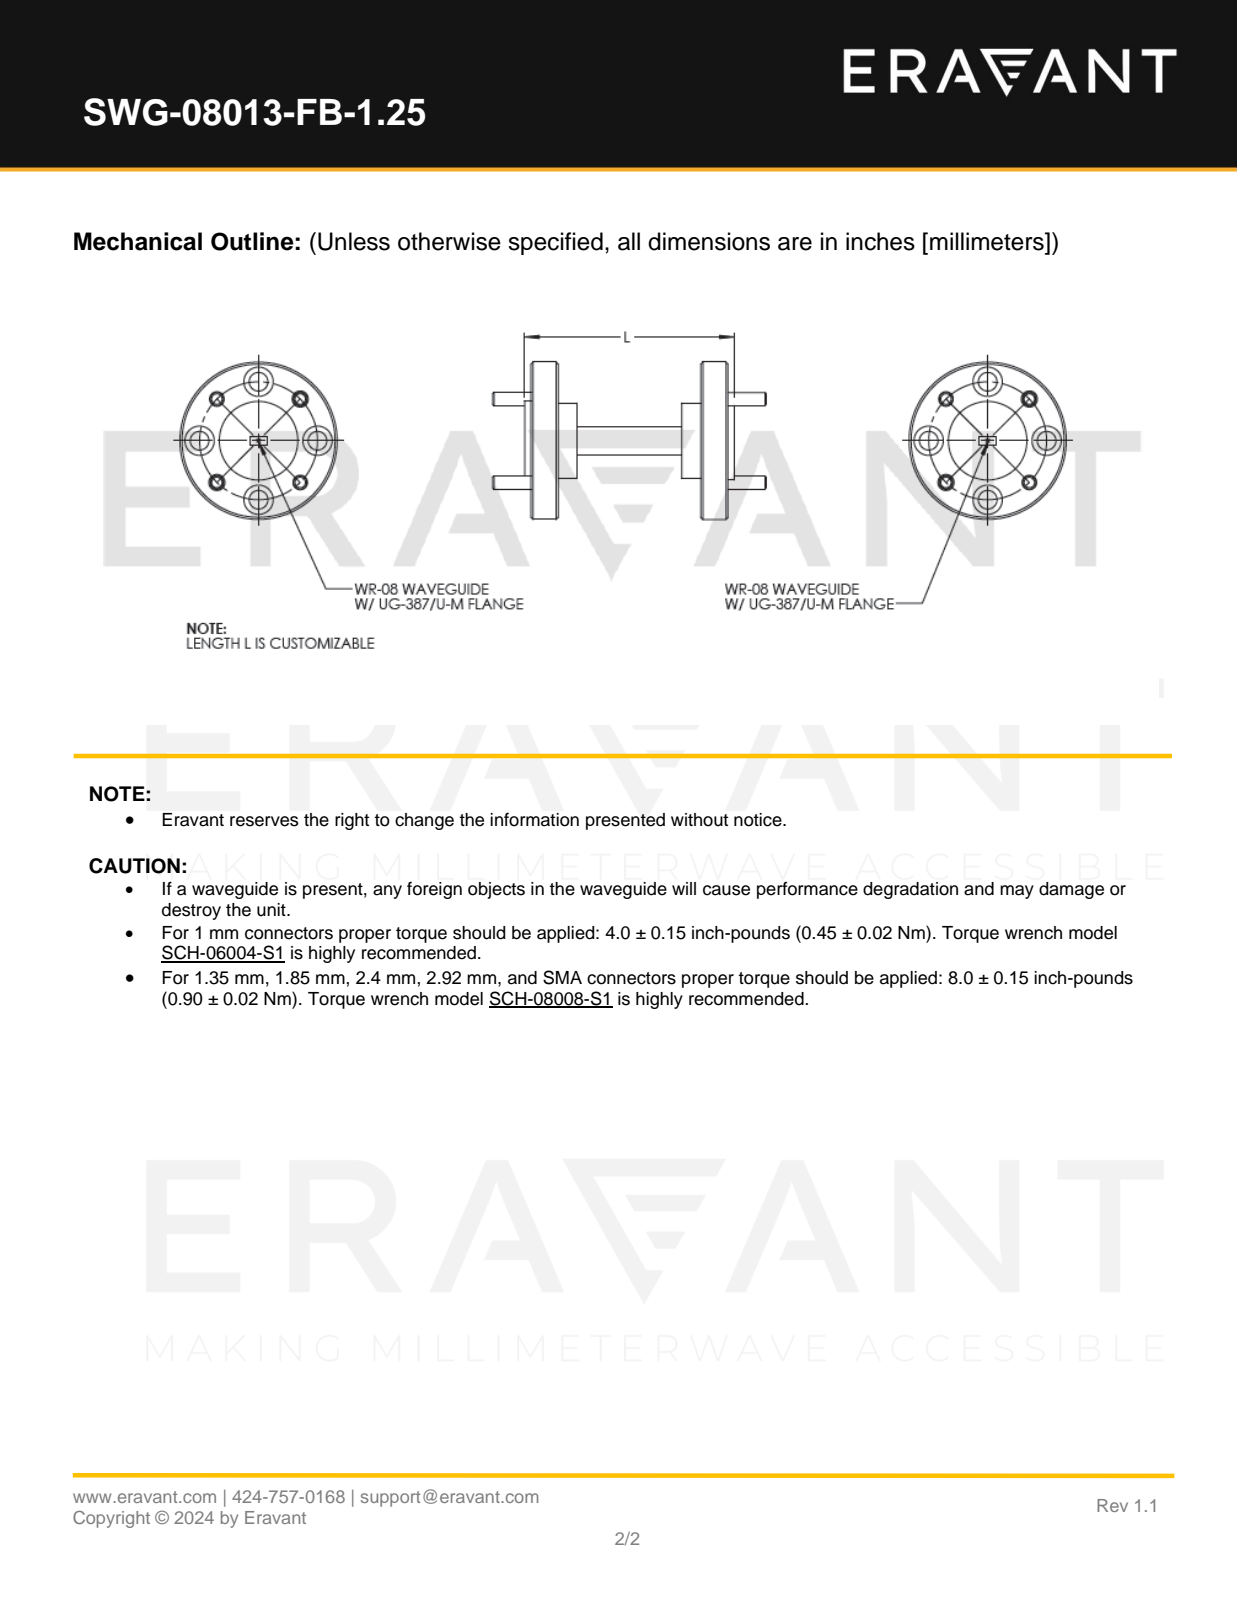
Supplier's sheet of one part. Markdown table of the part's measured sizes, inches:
| quantity | value |
| --- | --- |
| part name | SWG-08013-FB-1.25 |
| STEP written by | SolidWorks 2021 (CONFIG_CONTROL_DESIGN) |
| units | inches |
| bodies | 5 solids, 146 faces (38 planar, 68 cylindrical, 40 other) |
| overall size | 1.555 × 0.75 × 0.75 |
| volume | 0.149 in³ |
| surface area | 3.654 in² |
| round holes (diameter × count) | 0.06 × 4, 0.067 × 4, 0.089 × 4, 0.14 × 4 |
| round bosses / shafts (diameter × count) | 0.063 × 4, 0.75 × 1, 0.375 × 1, 0.36 × 1 |
| main face-to-face distances | 0.13, 1.06, 0.93, 1.19, 0.03, 0.16, 1.09, 1.22, 0.25, 1 |
| hole center spacings | 0.215, 0.398, 0.52, 0.563, 0.398, 0.519, 0.562 |
